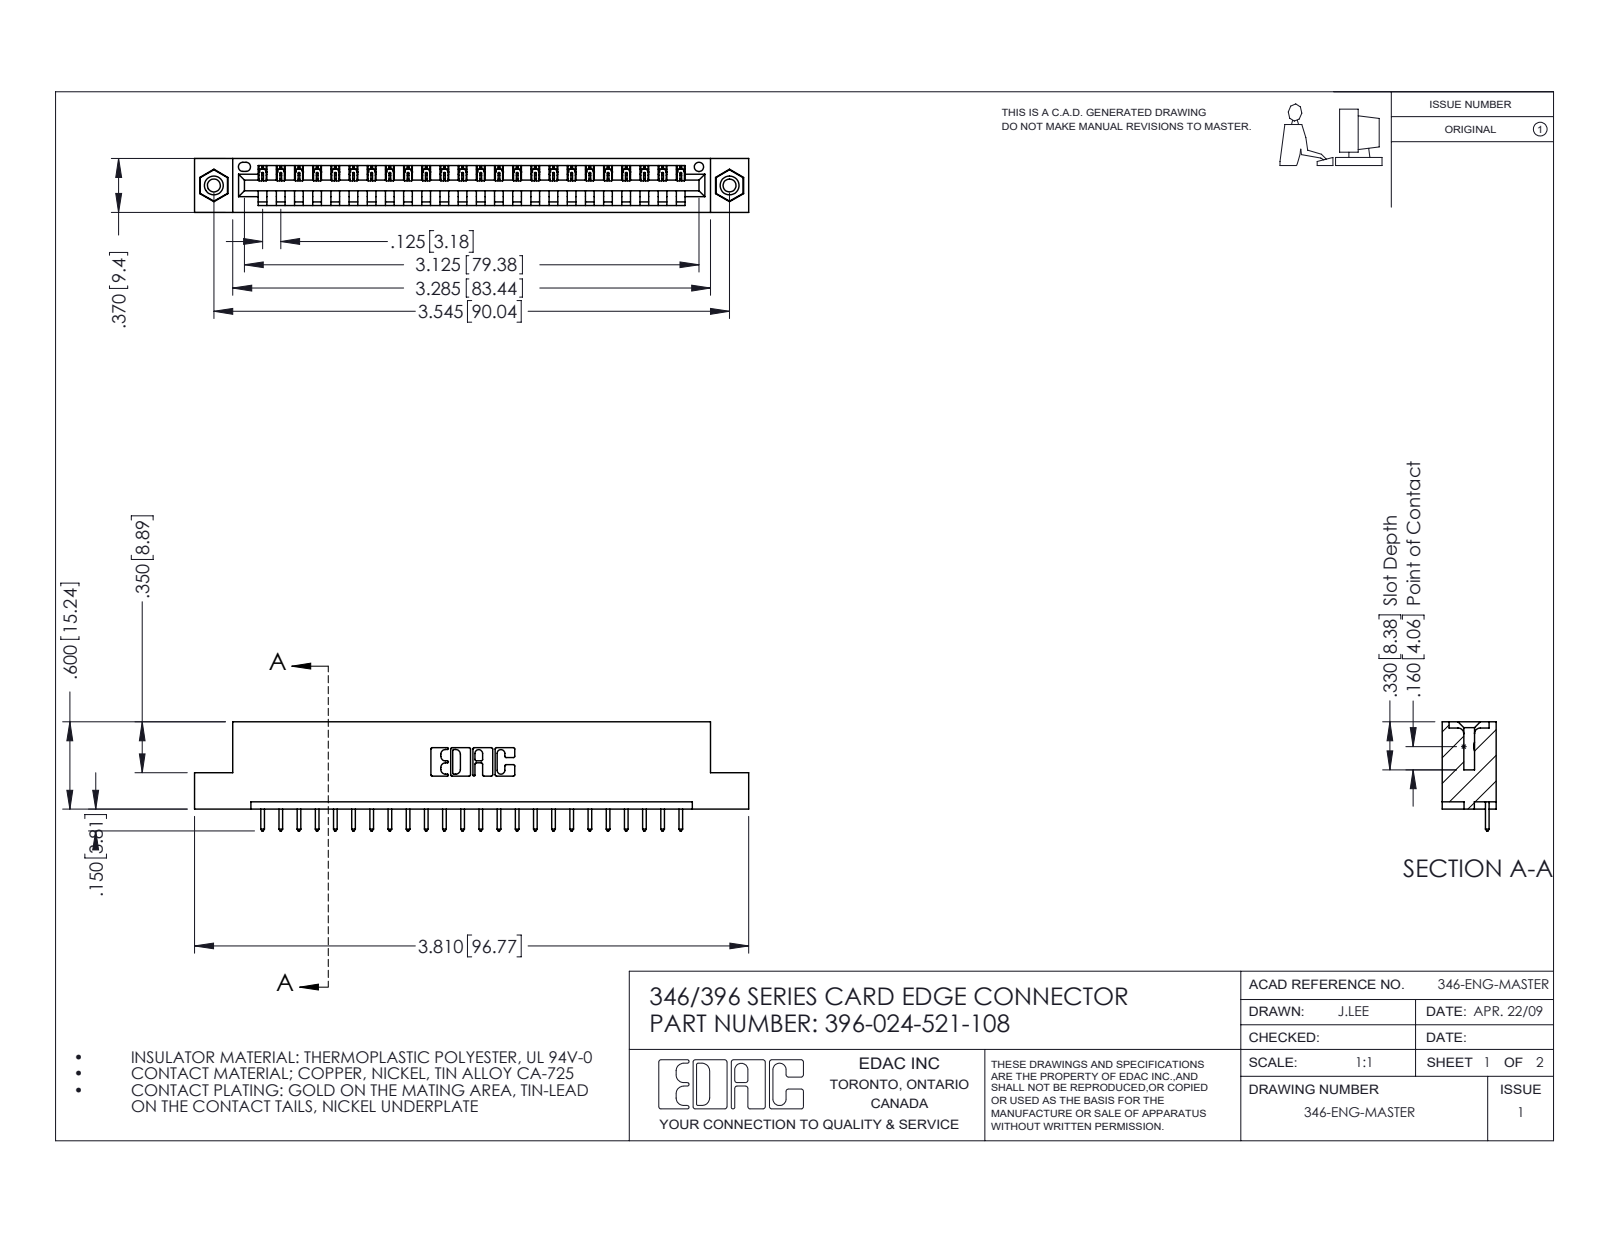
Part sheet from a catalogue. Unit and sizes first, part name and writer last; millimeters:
Units: millimetres
Overall size (bounding box): 96.8 × 19.1 × 9.4
Round holes (diameter × count): ⌀2.3 ×2, ⌀3.2 ×2, ⌀4 ×2, ⌀1.6 ×1
Round bosses / shafts (diameter × count): ⌀3.9 ×2
Partial cylindrical surfaces — rounded edges, fillets, slot ends (radius × count): R0.2 ×48, R0.3 ×48, R0.3 ×22, R0.2 ×6, R0.8 ×6, R0.7 ×3, R0.8 ×2, R1 ×2
Main face-to-face distances: 1.2, 8.2, 9.4, 6.4, 1.8, 7.6, 0.6, 3.8, 5.6, 2.5
Hole centre spacings: 6.2, 84.8, 90
Volume: 9 060 mm³ · Surface area: 10 880 mm²
Bodies: 27 solids, 1574 faces (1068 planar, 490 cylindrical, 16 other)
Part name (STEP PRODUCT): 396-024-521-108; 345-250-001_345-250-003-102; 345-292-001_345-293-121; 346 Part_Flush Mounting Lugs - 0.156 Dia-TI
STEP written by: SolidWorks 2016 (CONFIG_CONTROL_DESIGN)
